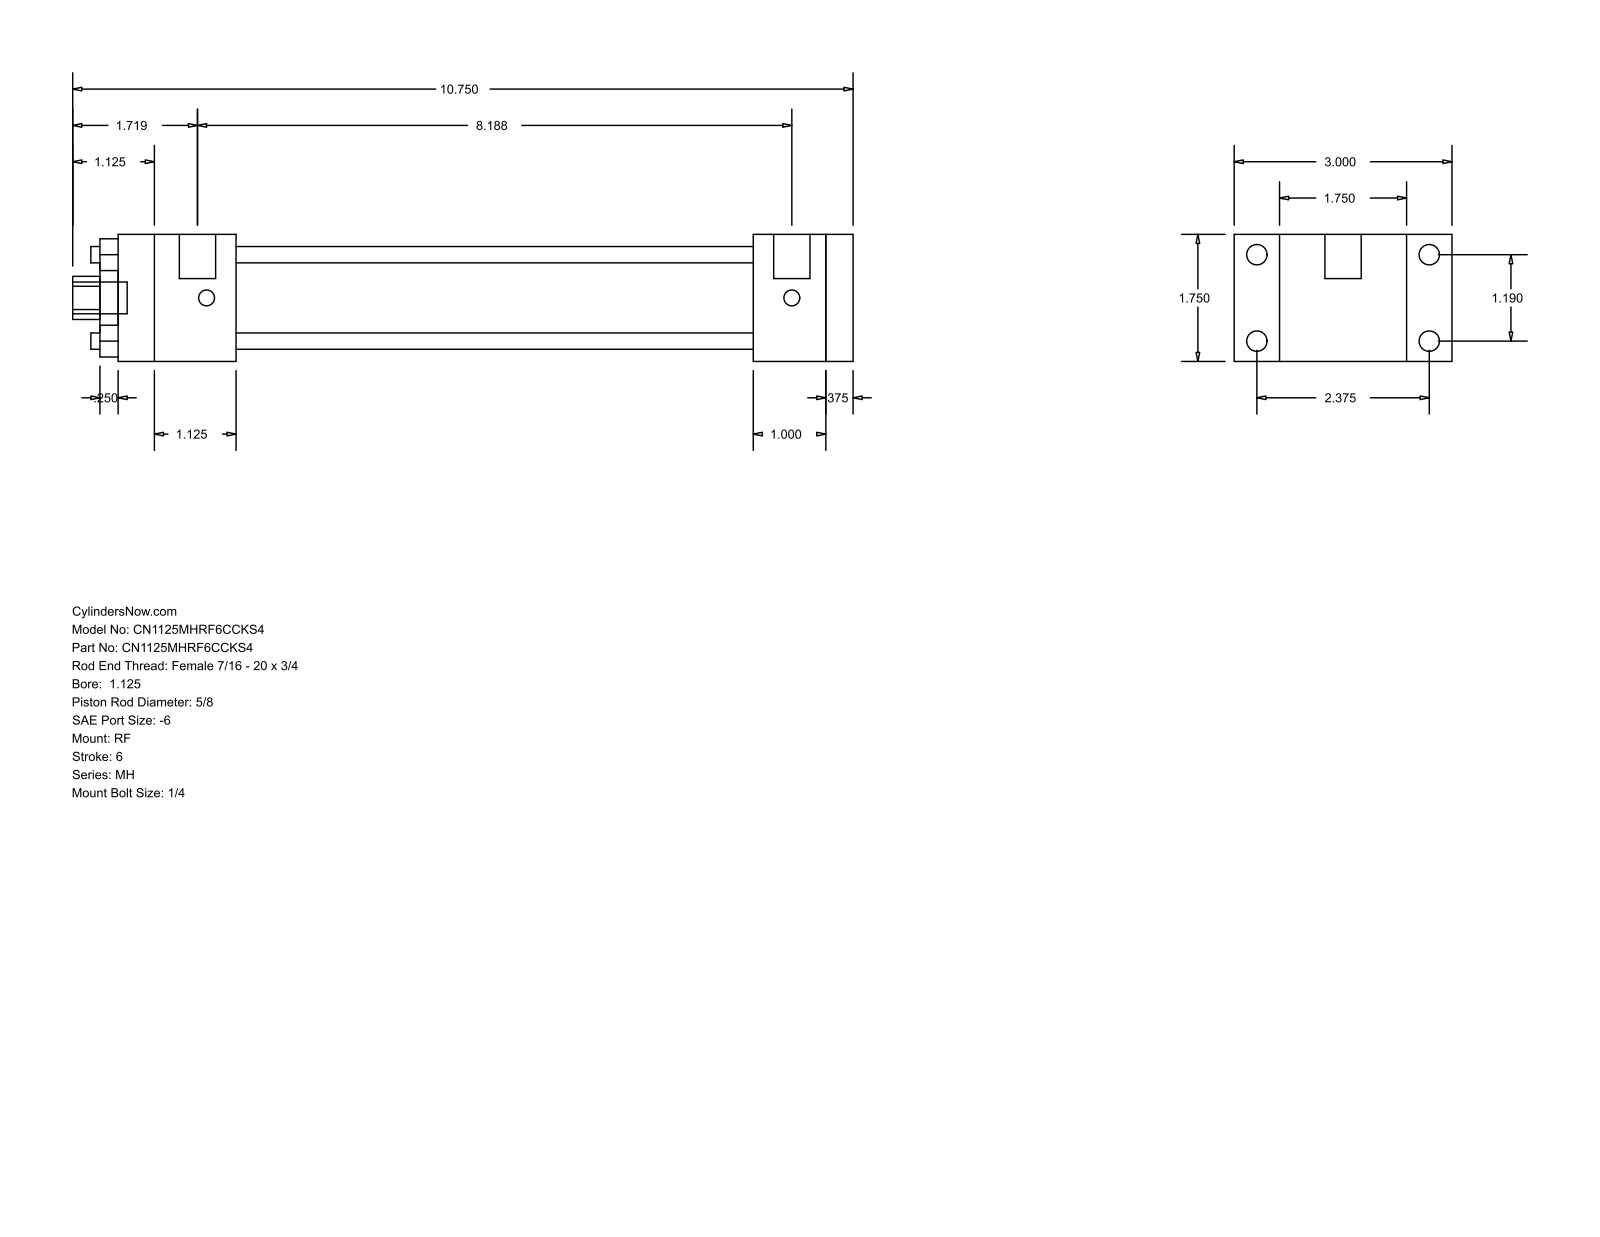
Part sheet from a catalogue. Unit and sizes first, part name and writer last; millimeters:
Units: millimetres
Overall size (bounding box): 273.05 × 76.2 × 44.45
Round holes (diameter × count): ⌀5.71 ×4, ⌀15.88 ×1, ⌀28.57 ×1, ⌀34.92 ×1
Round bosses / shafts (diameter × count): ⌀7.14 ×4, ⌀5.56 ×4, ⌀12.7 ×2, ⌀11.11 ×1
Partial cylindrical surfaces — rounded edges, fillets, slot ends (radius × count): R7.54 ×1
Main face-to-face distances: 44.46, 9.53, 257.17, 15.87, 206.37, 215.9, 180.97, 25.4, 34.93, 41.27
Hole centre spacings: 21.37, 30.22, 42.74
Bodies: 0 solids, 92 faces (64 planar, 28 cylindrical, 0 other)
Part name (STEP PRODUCT): MH_RF__0112_0.625
STEP written by: GSSL Pune (CONFIG_CONTROL_DESIGN)
